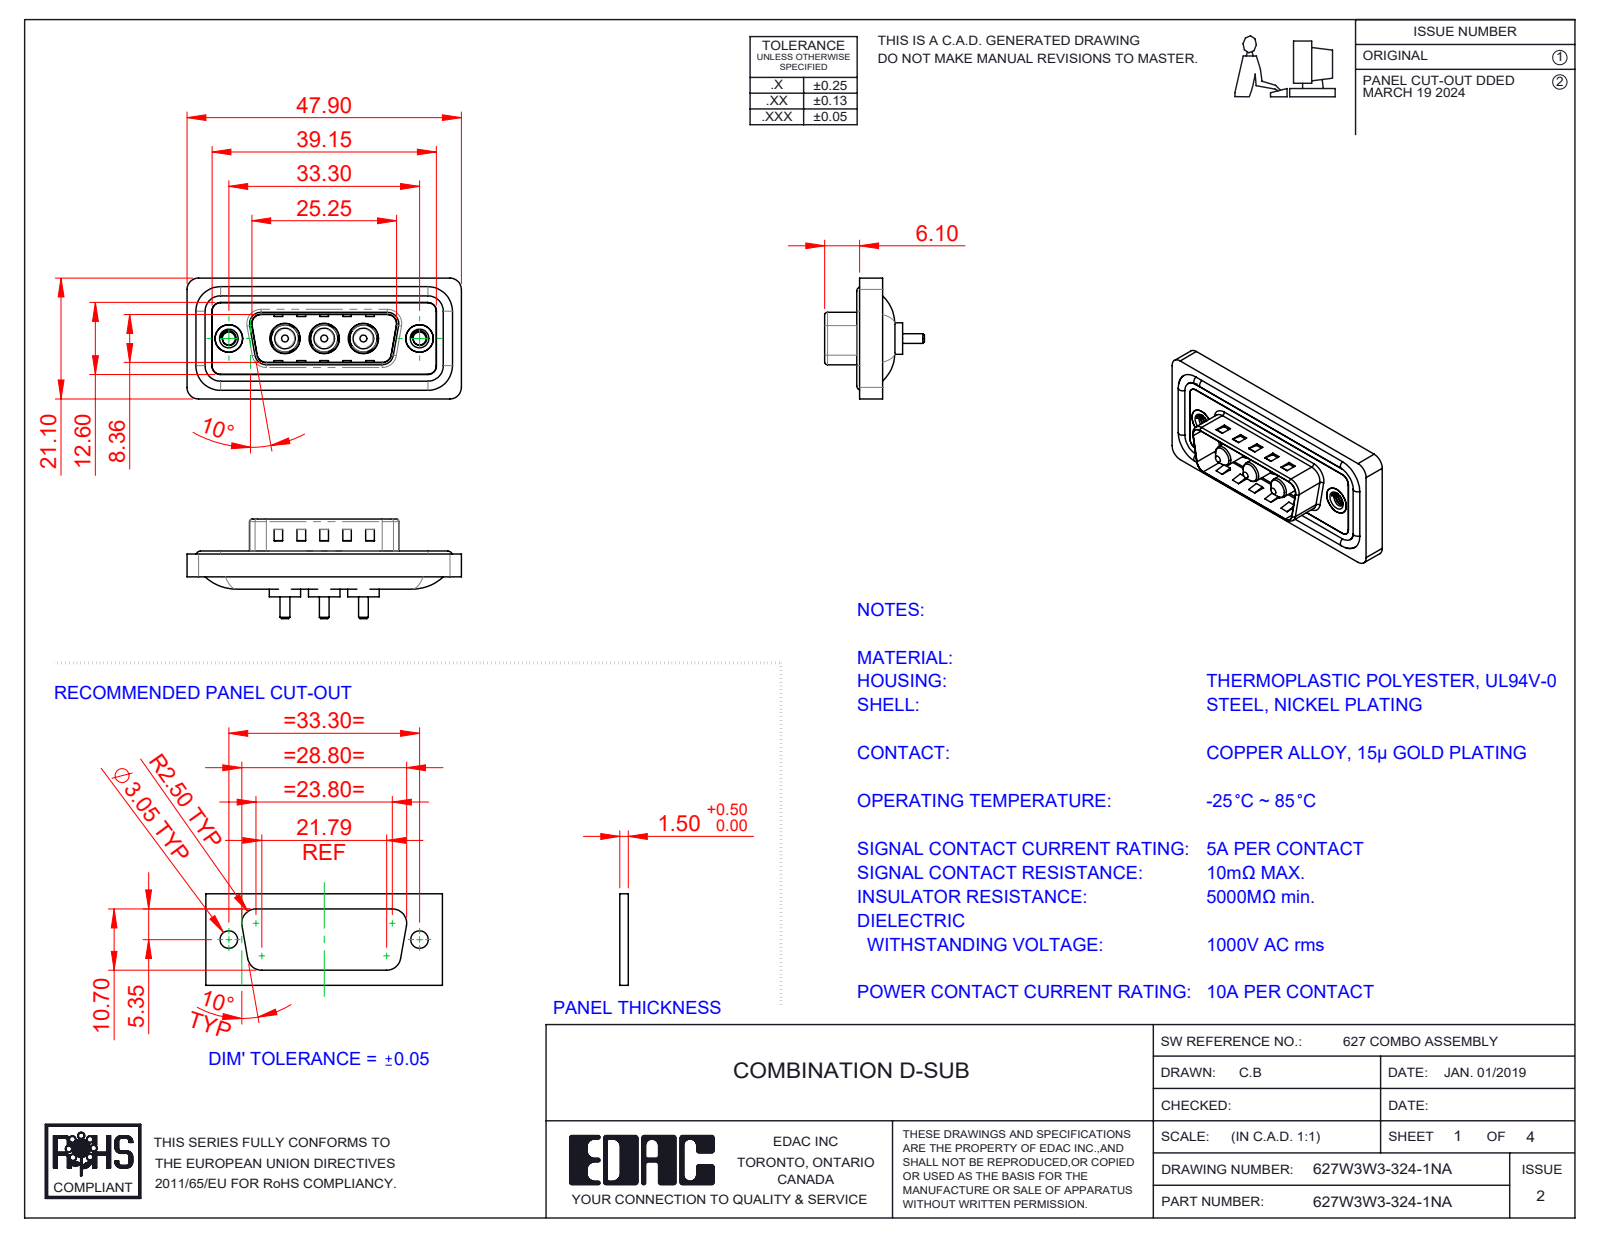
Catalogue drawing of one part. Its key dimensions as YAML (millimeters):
part_name: "627Combo Waterproof Housing_15 Contacts; 627Combo Threaded Rivet_A; Power Pin_10A S; 627Combo Housing_3W3 (+3 more)"
step_written_by: "SolidWorks 2023 (CONFIG_CONTROL_DESIGN)"
units: millimeters
bodies: {solids: 13, faces: 562, planar: 207, cylindrical: 243, other: 112}
overall_size: [47.9, 21.1, 17.4]
volume: 5543
surface_area: 8713
round_holes:
  - {diameter: 4.85, count: 3}
  - {diameter: 5.3, count: 3}
  - {diameter: 2.26, count: 2}
  - {diameter: 4, count: 2}
  - {diameter: 4.8, count: 2}
  - {diameter: 5, count: 2}
round_bosses_or_shafts:
  - {diameter: 1.6, count: 4}
  - {diameter: 5.5, count: 3}
  - {diameter: 5.2, count: 3}
  - {diameter: 4.75, count: 3}
  - {diameter: 3.75, count: 3}
  - {diameter: 3.6, count: 3}
  - {diameter: 1.7, count: 3}
  - {diameter: 4.9, count: 2}
partial_cylinders:
  - {radius: 1.5, count: 26}
  - {radius: 2, count: 20}
  - {radius: 0.5, count: 8}
  - {radius: 1.6, count: 8}
  - {radius: 0.25, count: 4}
  - {radius: 0.6, count: 4}
  - {radius: 0.65, count: 4}
  - {radius: 0.9, count: 4}
face_to_face_distances: [0.4, 1.5, 1.1, 0.5, 1.6, 3.1, 2.9, 4, 0.82, 9.58]
hole_center_spacings: [6.85, 9.8, 16.65, 23.5, 13.7, 33.3]
